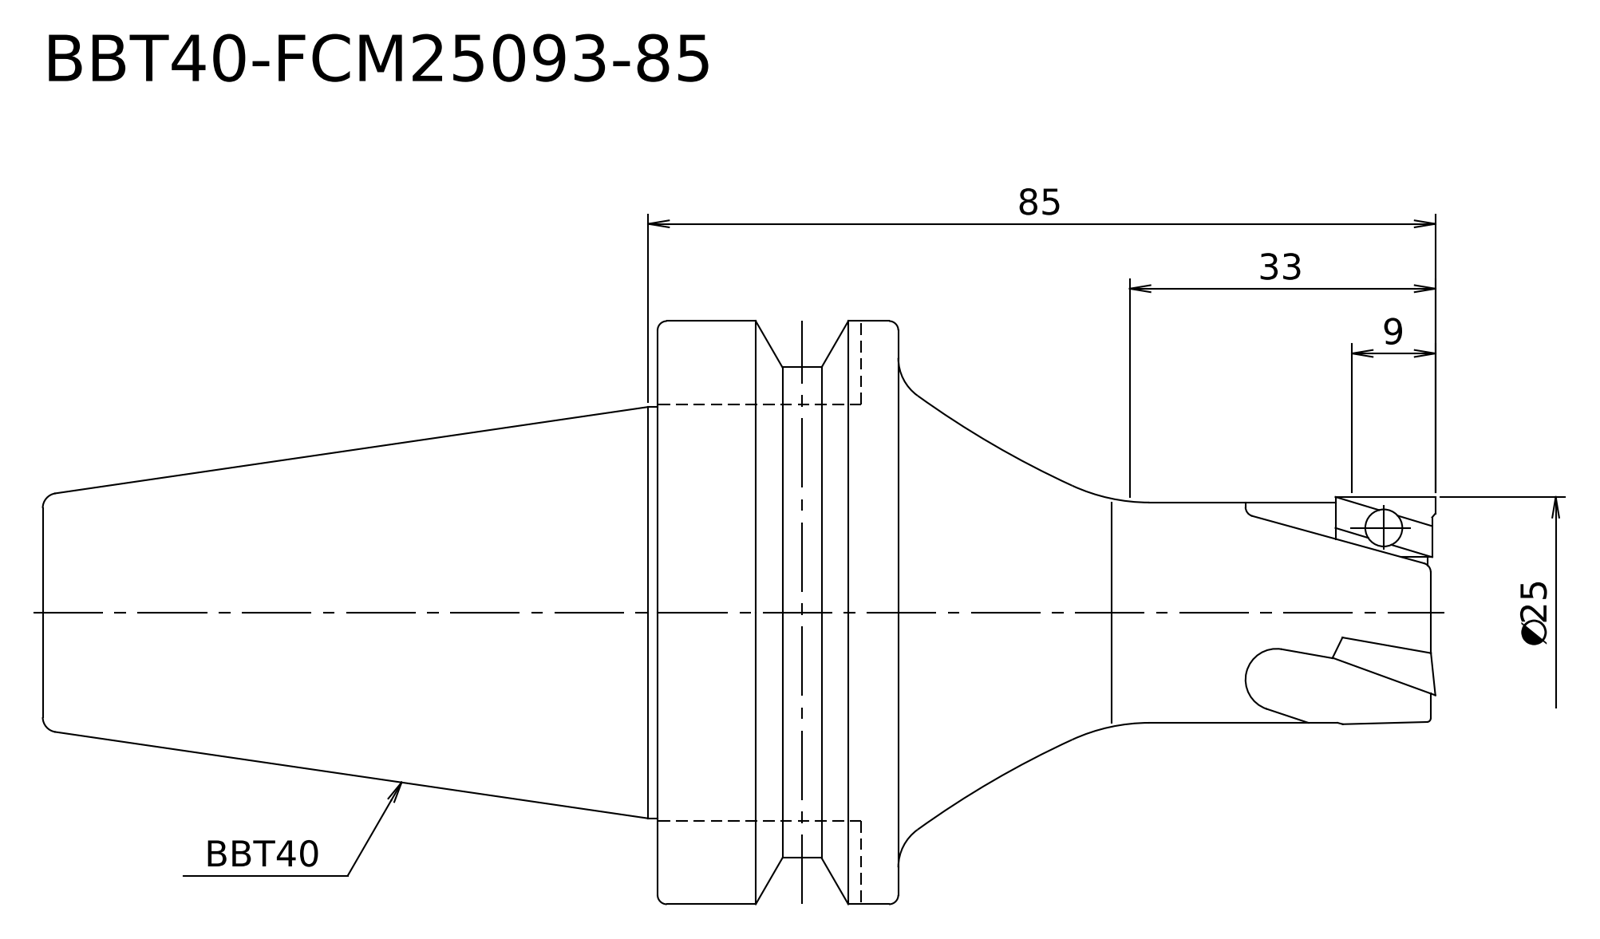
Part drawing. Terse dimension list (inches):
written by: Kubotek KeyCreator V8.5.1 (14335) (CONFIG_CONTROL_DESIGN)
unit: in
bodies: 1 solid, 17 faces (4 planar, 6 cylindrical, 7 other)
size: 5.921 × 2.48 × 2.48
volume: 11.07 in³; area: 35.18 in²
bosses: 1× ⌀2.48, 1× ⌀2.087, 1× ⌀1.75, 1× ⌀0.984, 1× ⌀0.937
face distances: 1.024, 3.638, 2.614, 2.283, 3.307, 5.921
